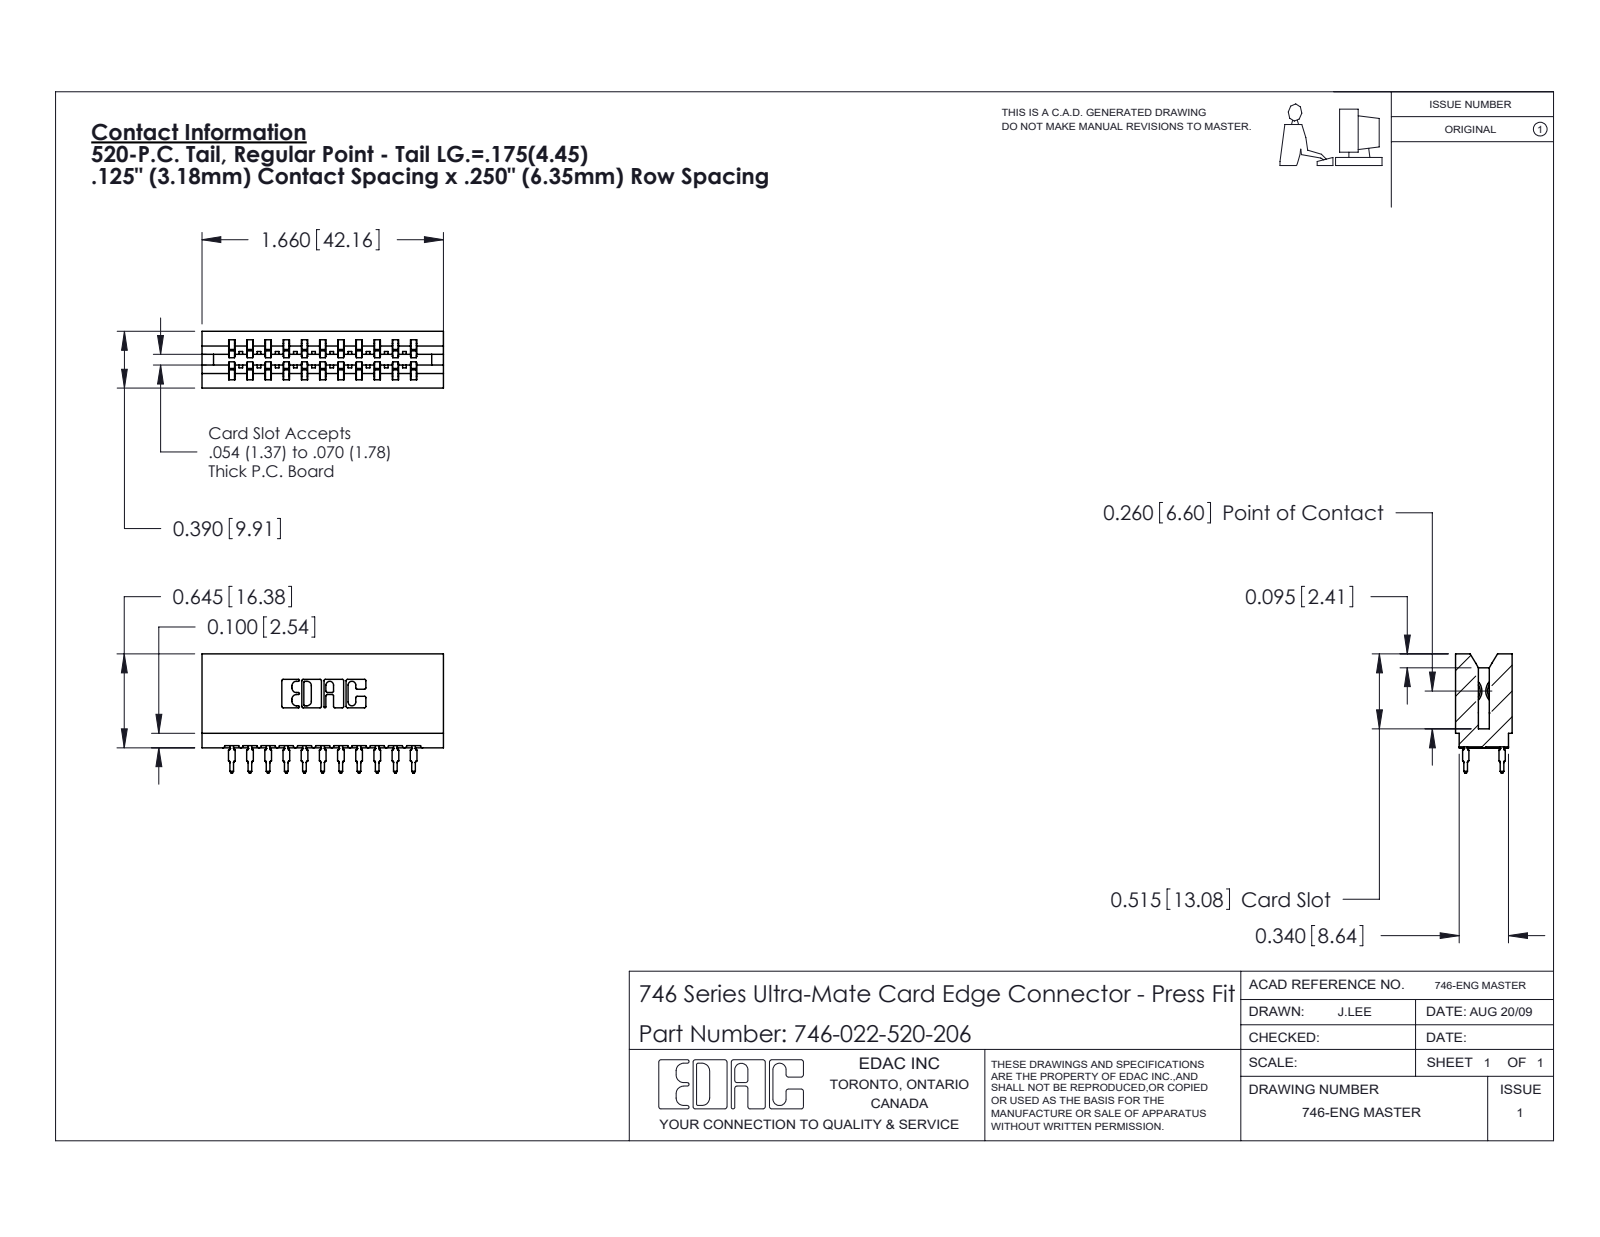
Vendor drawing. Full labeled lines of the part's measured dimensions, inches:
Part name (STEP PRODUCT): 746-292-001_520; 746-022-520-206; 746 Part_.515 Slot Depth - 06
STEP written by: SolidWorks 2020 (CONFIG_CONTROL_DESIGN)
Units: inches
Bodies: 23 solids, 2067 faces (1068 planar, 427 cylindrical, 572 other)
Overall size (bounding box): 1.66 × 0.819 × 0.39
Volume: 0.285 in³ · Surface area: 10.55 in²
Partial cylindrical surfaces — rounded edges, fillets, slot ends (radius × count): R0.021 ×44, R0.01 ×22, R0.015 ×12, R0.005 ×8, R0.011 ×8, R0.007 ×6, R0.031 ×6, R0.026 ×3
Main face-to-face distances: 0.25, 0.333, 0.5, 0.057, 0.125, 0.125, 0.39, 0.042, 0.208, 0.458
